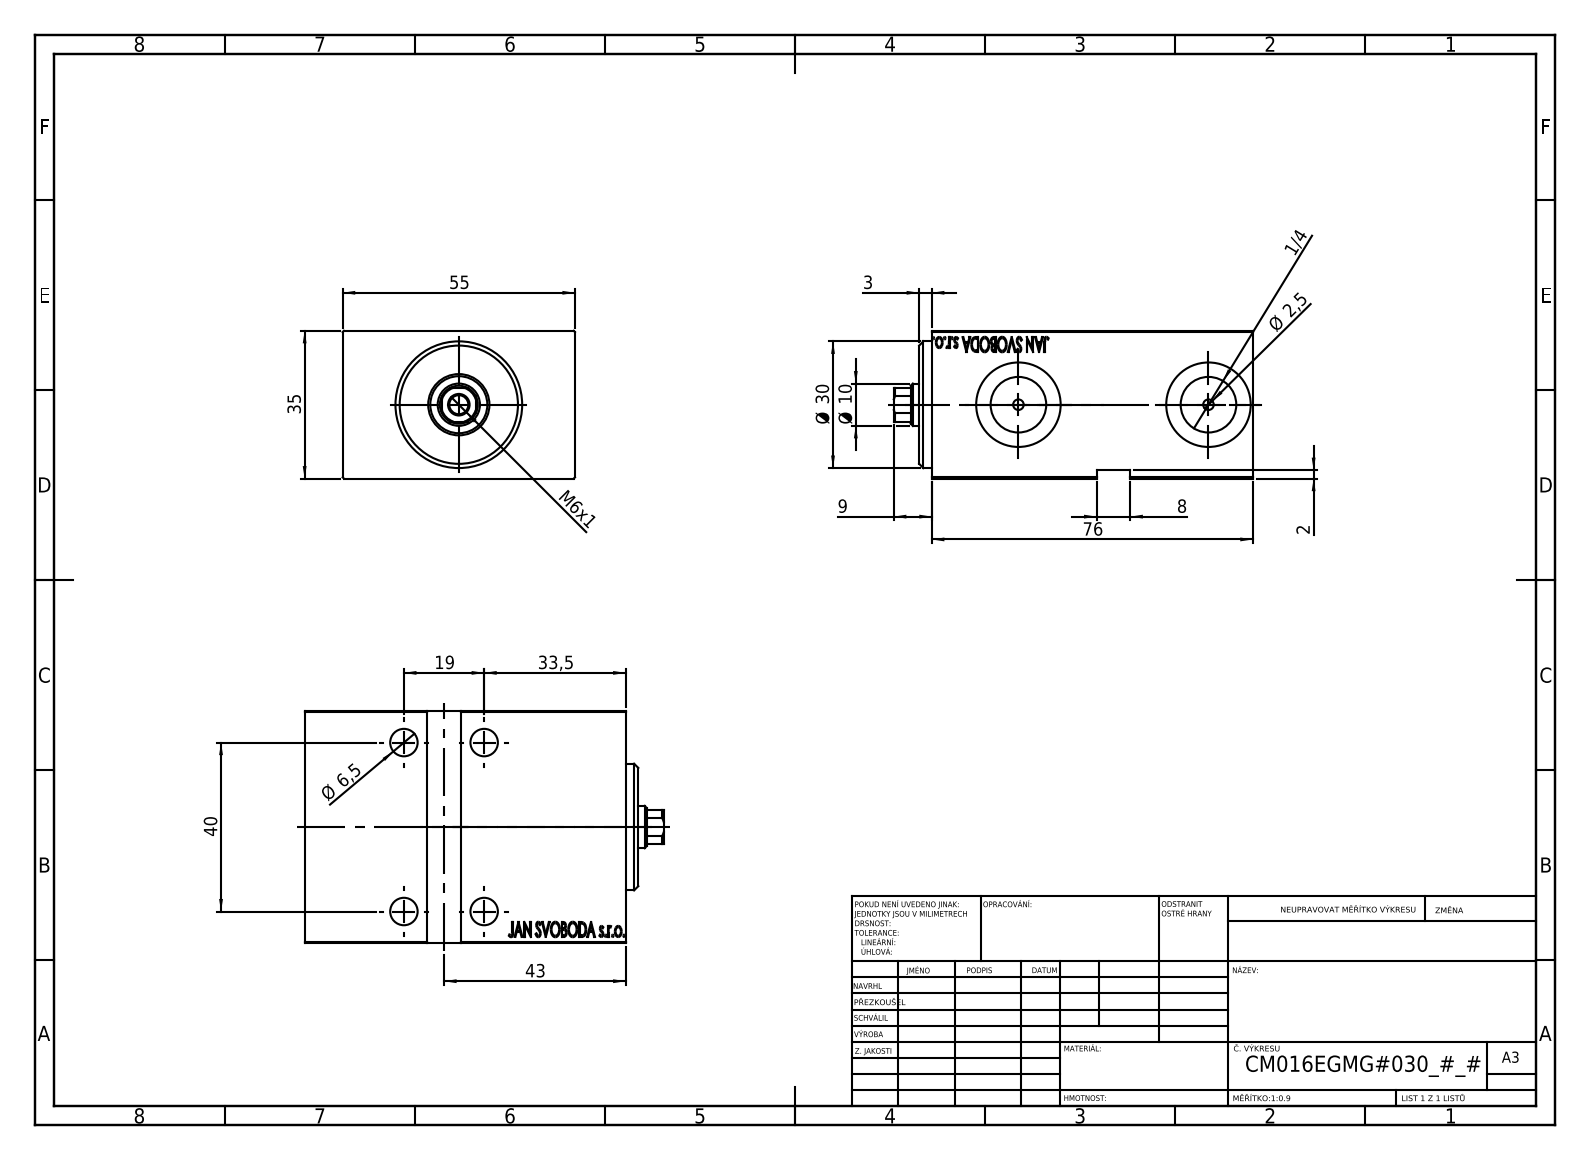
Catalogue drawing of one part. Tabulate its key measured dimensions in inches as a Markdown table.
| quantity | value |
| --- | --- |
| part name | V450CM_VC_B; V450CM_E_Body; V450CM_E_VCP |
| STEP written by | SolidWorks 2019 (CONFIG_CONTROL_DESIGN) |
| units | inches |
| bodies | 3 solids, 859 faces (411 planar, 54 cylindrical, 394 other) |
| overall size | 3.346 × 2.165 × 1.378 |
| volume | 8.237 in³ |
| surface area | 50.45 in² |
| round holes (diameter × count) | 0.256 × 4, 0.413 × 4, 0.098 × 2, 0.518 × 2, 0.787 × 2, 0.177 × 1, 0.394 × 1, 0.531 × 1, 0.571 × 1, 0.63 × 1, 0.984 × 1 |
| round bosses / shafts (diameter × count) | 1.181 × 1, 0.709 × 1 |
| partial cylindrical surfaces (radius × count) | 0.177 × 1 |
| main face-to-face distances | 1.378, 2.165, 2.992, 0.197, 2.795, 1.654, 0.315, 0.118, 3.11, 0.079 |
| hole center spacings | 0.748, 1.575, 1.743, 1.772 |
